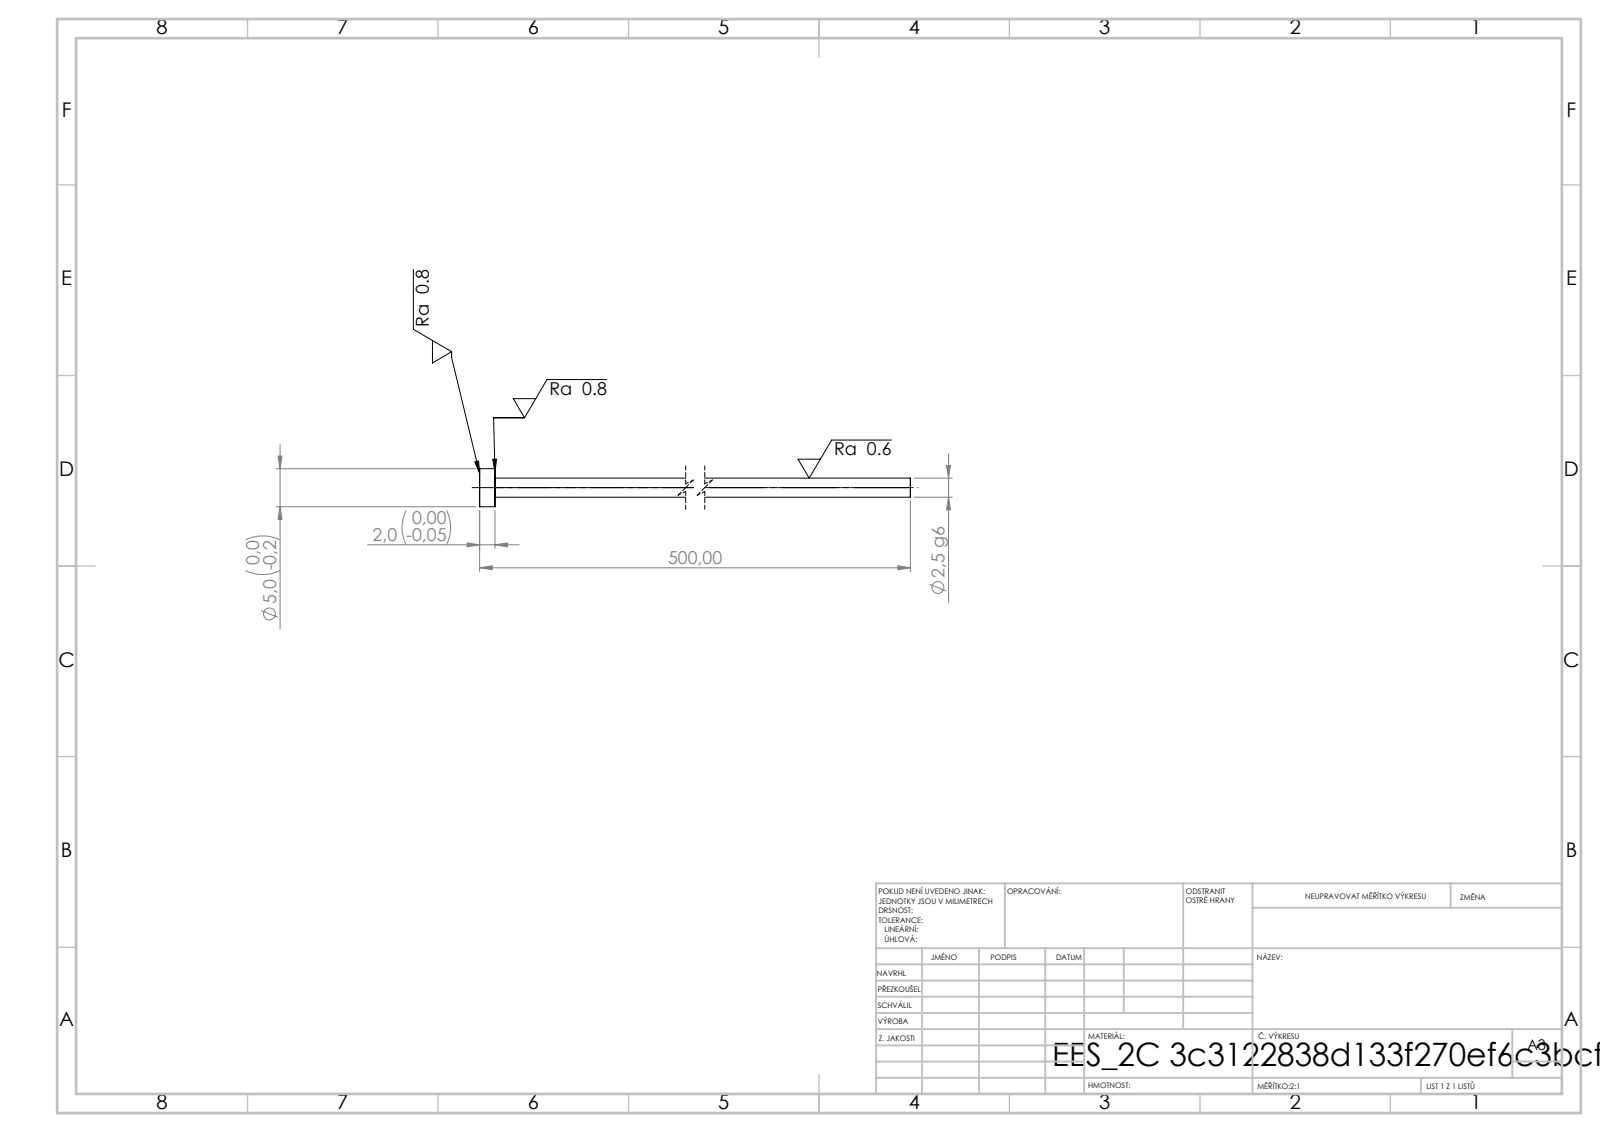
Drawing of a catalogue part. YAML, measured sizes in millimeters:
step_written_by: "SolidWorks 2019 (CONFIG_CONTROL_DESIGN)"
units: millimeters
bodies: {solids: 1, faces: 7, planar: 3, cylindrical: 4, other: 0}
overall_size: [500, 5, 5]
volume: 2484
surface_area: 3982
round_bosses_or_shafts:
  - {diameter: 5, count: 1}
  - {diameter: 2.5, count: 1}
face_to_face_distances: [2, 500, 498]
